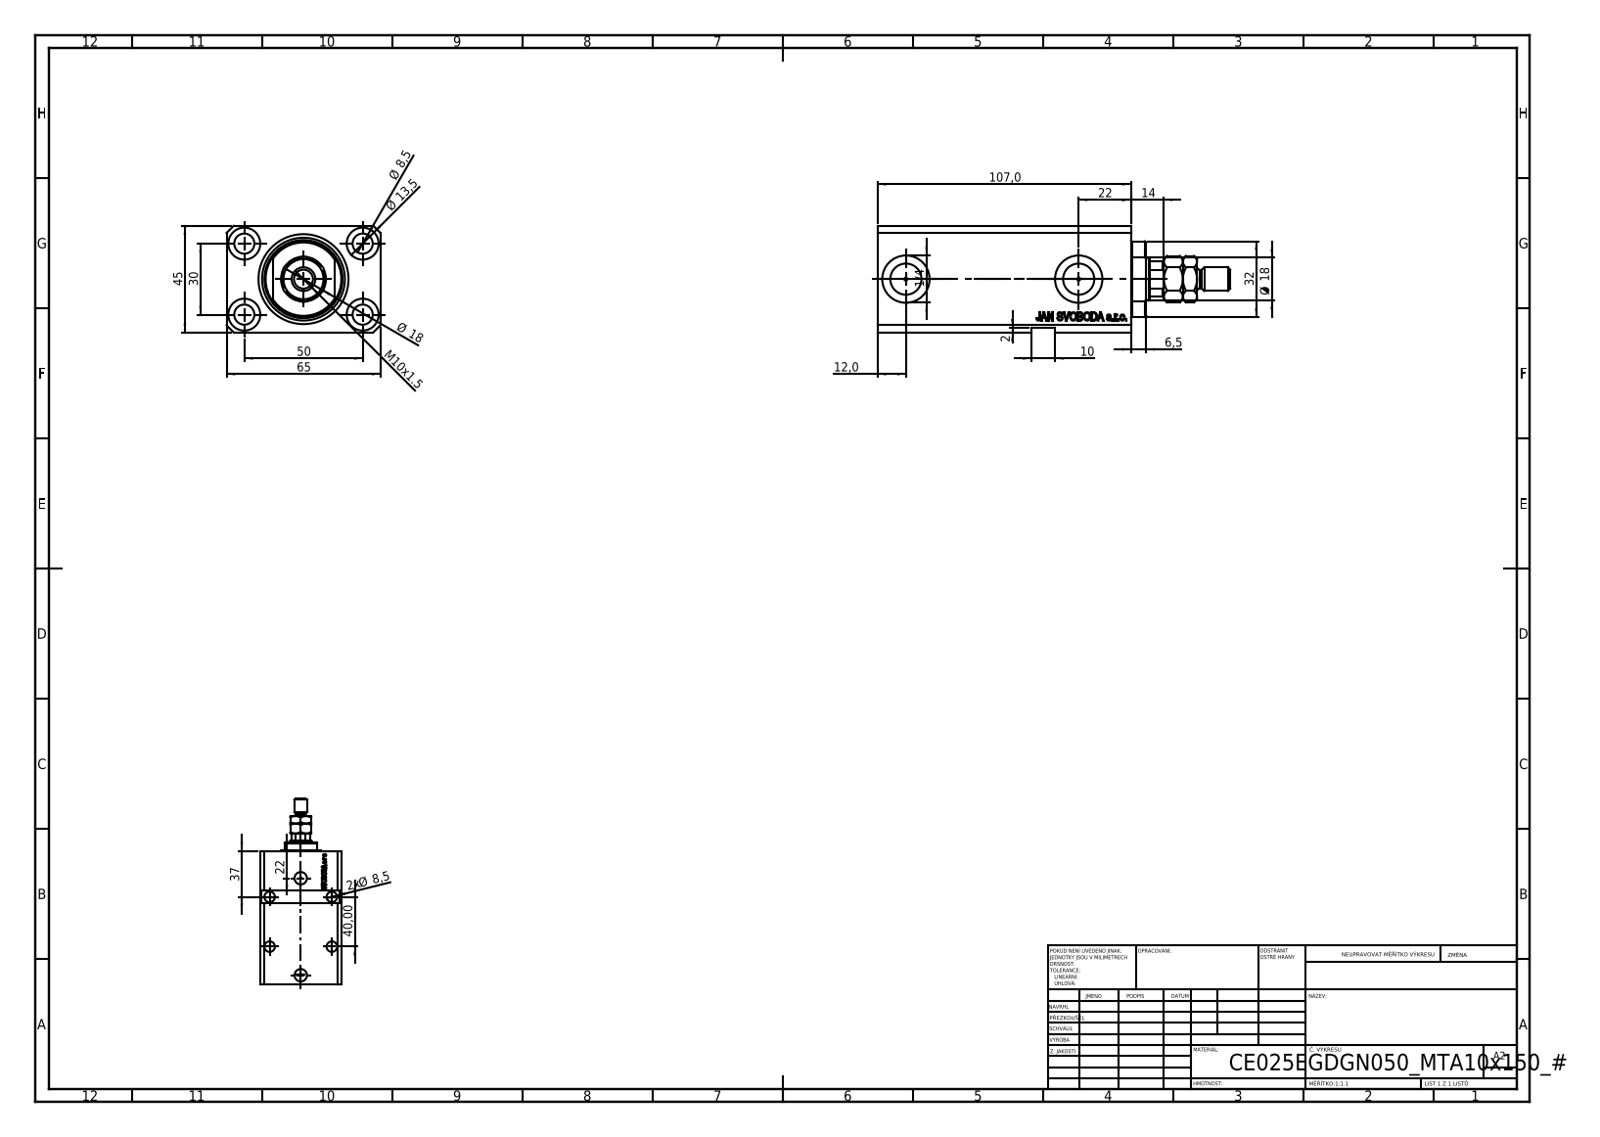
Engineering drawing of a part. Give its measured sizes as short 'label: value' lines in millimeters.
name: MTA; V250CE_C_VCP; V250CE_E_Body; V250CE_VC_E
written by: SolidWorks 2019 (CONFIG_CONTROL_DESIGN)
unit: mm
bodies: 4 solids, 982 faces (454 planar, 120 cylindrical, 408 other)
size: 149 × 65 × 45
volume: 262 423 mm³; area: 69 800 mm²
holes: 9× ⌀8.5, 4× ⌀1.25, 4× ⌀13.5, 2× ⌀10, 2× ⌀13.16, 2× ⌀20, 1× ⌀18, 1× ⌀25, 1× ⌀38
bosses: 1× ⌀10, 1× ⌀8
rounds: 1× R8.5, 1× R16
face distances: 45, 65, 14, 93, 107, 6.9, 86.1, 100.1, 43, 28
hole spacings: 29.15, 50, 30, 33.61, 33.97, 40, 58.31, 60.42
